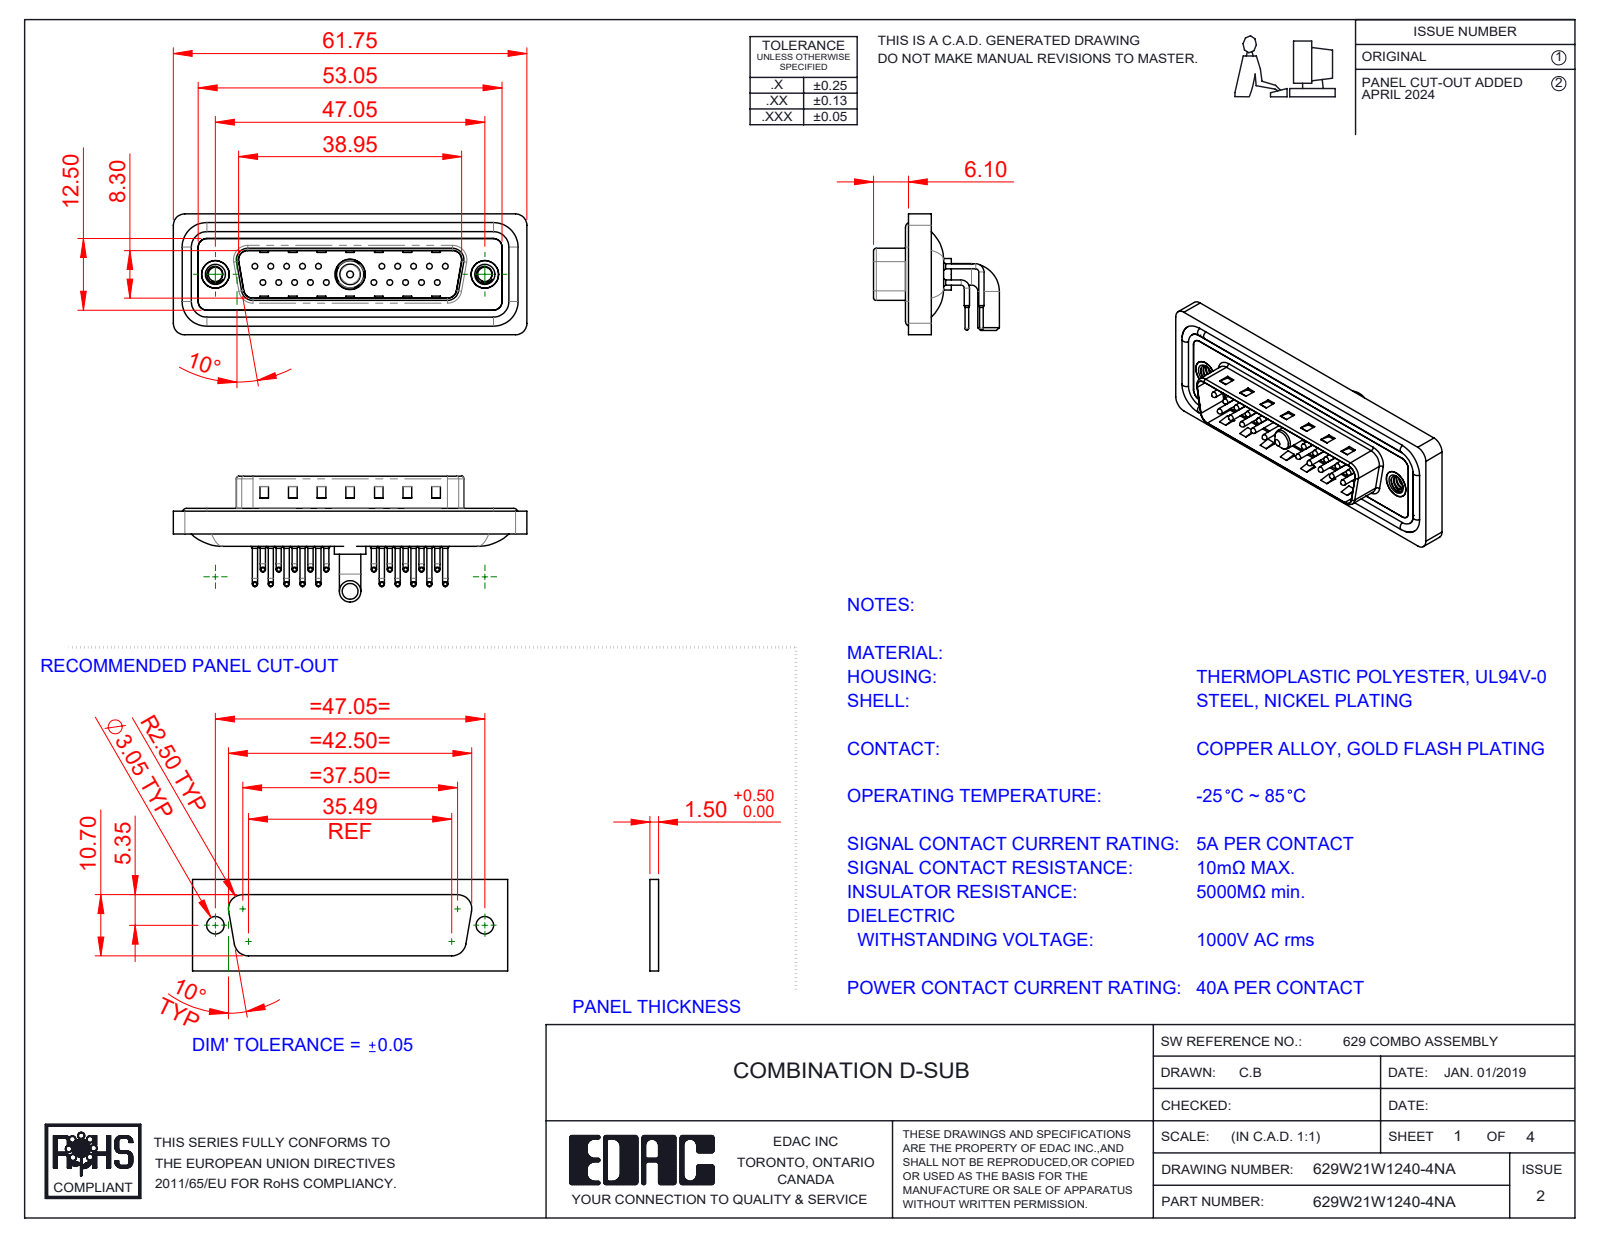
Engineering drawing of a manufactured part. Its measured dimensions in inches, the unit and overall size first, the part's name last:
Units: inches
Overall size (bounding box): 2.431 × 0.865 × 0.831
Round holes (diameter × count): ⌀0.03 ×20, ⌀0.063 ×20, ⌀0.079 ×20, ⌀0.098 ×2, ⌀0.157 ×2, ⌀0.189 ×2, ⌀0.197 ×2, ⌀0.191 ×1, ⌀0.209 ×1
Round bosses / shafts (diameter × count): ⌀0.035 ×40, ⌀0.059 ×20, ⌀0.039 ×20, ⌀0.026 ×20, ⌀0.063 ×4, ⌀0.193 ×2, ⌀0.148 ×2, ⌀0.217 ×1
Partial cylindrical surfaces — rounded edges, fillets, slot ends (radius × count): R0.04 ×20, R0.059 ×18, R0.079 ×18, R0.02 ×8, R0.063 ×8, R0.01 ×4, R0.024 ×4, R0.026 ×4
Main face-to-face distances: 0.016, 0.114, 0.031, 0.161, 0.043, 0.083, 0.063, 0.177, 0.059, 0.098
Hole centre spacings: 0.124, 0.109, 0.218, 0.327, 0.198, 0.763, 0.826, 0.872
Volume: 0.457 in³ · Surface area: 19.79 in²
Bodies: 29 solids, 2720 faces (1499 planar, 927 cylindrical, 294 other)
Part name (STEP PRODUCT): 629Combo Waterproof Housing_25 Contacts; 629Combo Shell Rear_25 Contacts; 629Combo Shell Front_25 Contacts; 629Combo Threaded Rivet_A (+5 more)
STEP written by: SolidWorks 2023 (CONFIG_CONTROL_DESIGN)
